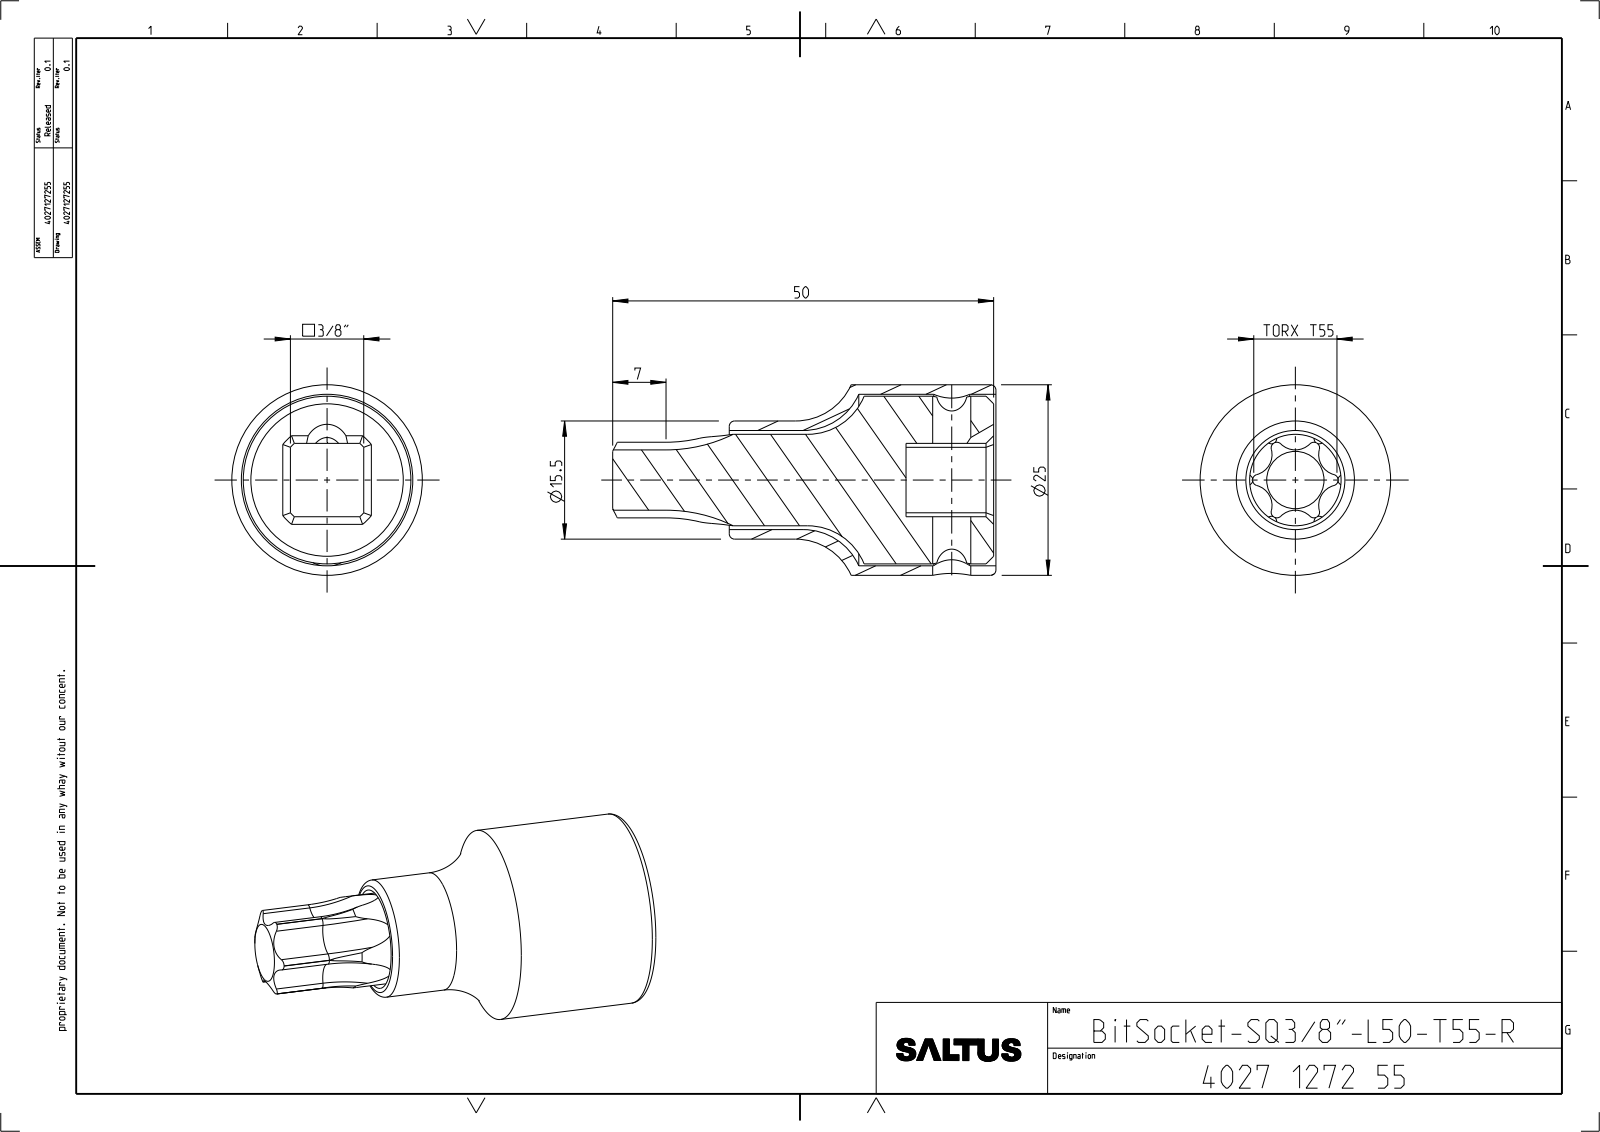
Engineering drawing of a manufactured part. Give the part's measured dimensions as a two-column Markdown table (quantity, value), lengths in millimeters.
| quantity | value |
| --- | --- |
| part name | 4027122655; 4027041664; 4027127255_ASM |
| STEP written by | CREO PARAMETRIC BY PTC INC, 2022414 (CONFIG_CONTROL_DESIGN) |
| units | millimeters |
| bodies | 2 solids, 110 faces (14 planar, 51 cylindrical, 45 other) |
| overall size | 50.3 × 25 × 25 |
| volume | 11 549 mm³ |
| surface area | 8 256 mm² |
| round holes (diameter × count) | 5 × 1, 13 × 1, 22.5 × 1 |
| round bosses / shafts (diameter × count) | 25 × 1, 22 × 1, 15.5 × 1, 12 × 1 |
| partial cylindrical surfaces (radius × count) | 0.73 × 12, 2.71 × 6, 3 × 1, 5.61 × 1, 6.45 × 1 |
| main face-to-face distances | 9.62, 11.5, 50, 38.5, 11.8, 50.3, 35, 34.7, 23.2, 15.3 |
